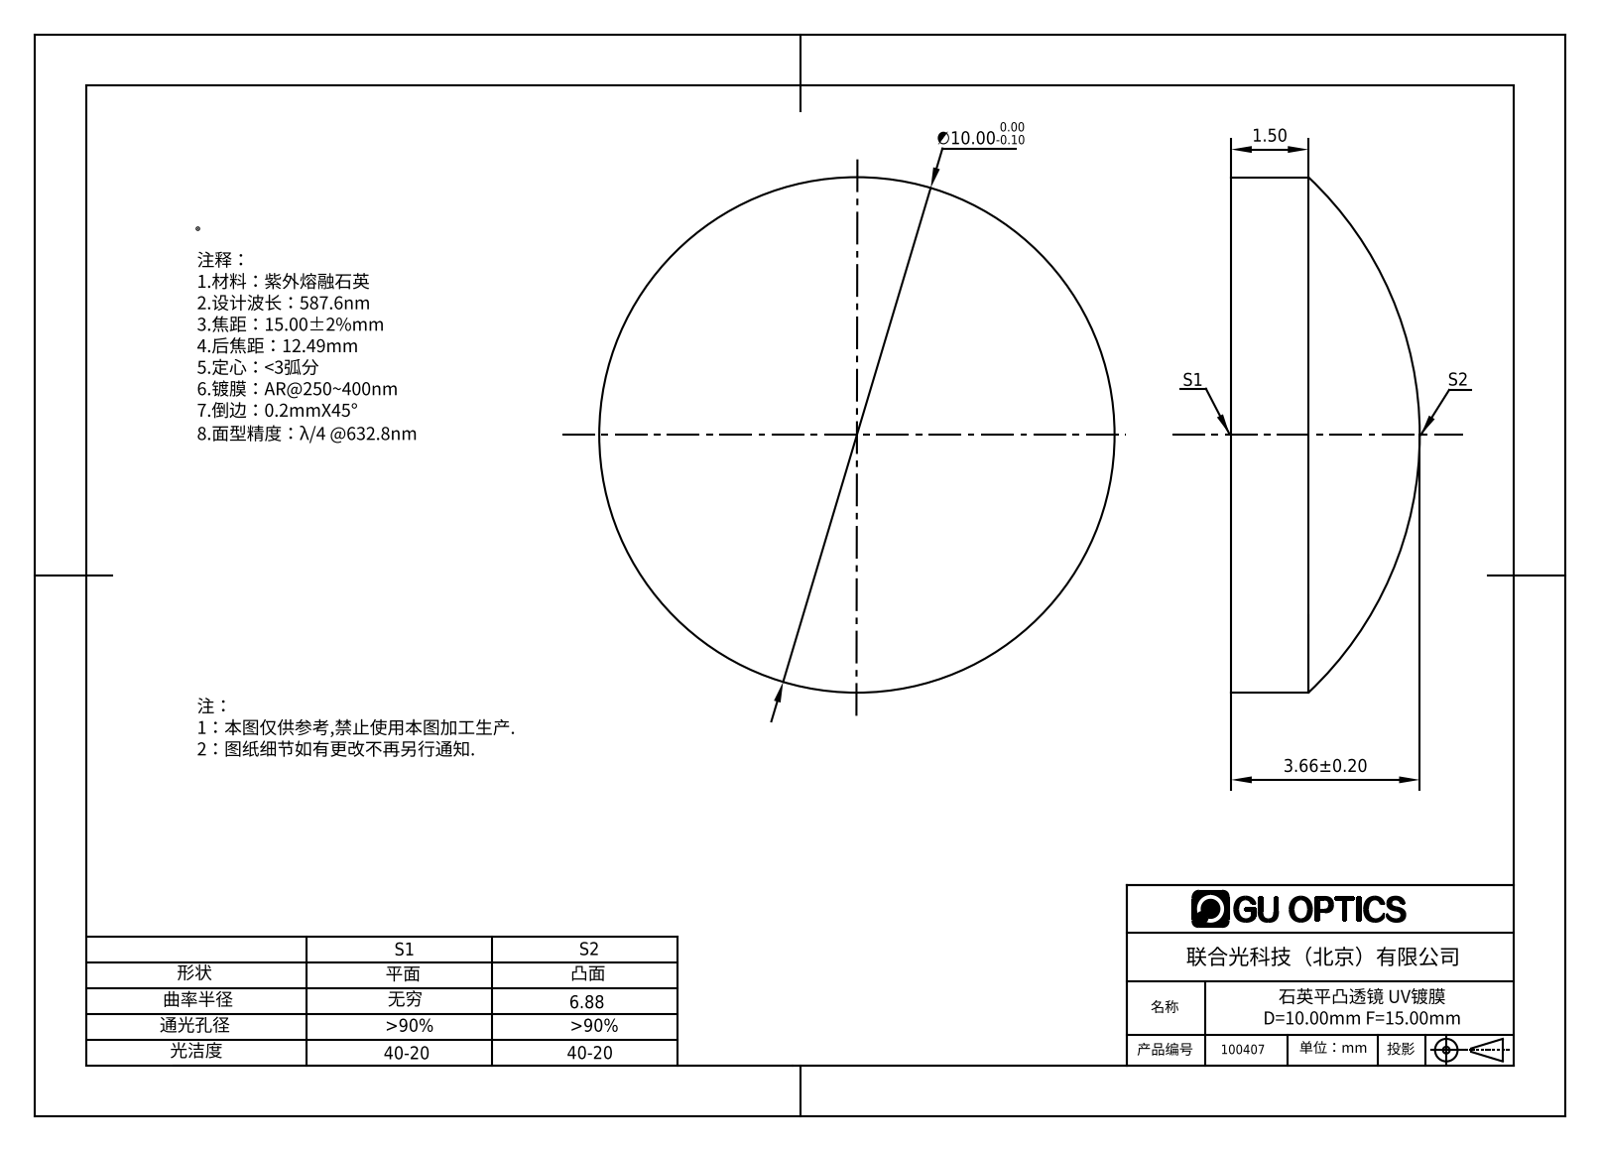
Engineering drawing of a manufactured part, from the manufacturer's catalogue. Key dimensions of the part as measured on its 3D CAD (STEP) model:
Part name (STEP PRODUCT): 100357
STEP written by: SolidWorks 2016 (AUTOMOTIVE_DESIGN)
Units: millimetres
Bodies: 1 solid, 5 faces (1 planar, 2 cylindrical, 2 other)
Overall size (bounding box): 10 × 10 × 3.66
Volume: 208 mm³ · Surface area: 219 mm²
Round bosses / shafts (diameter × count): ⌀10 ×1
